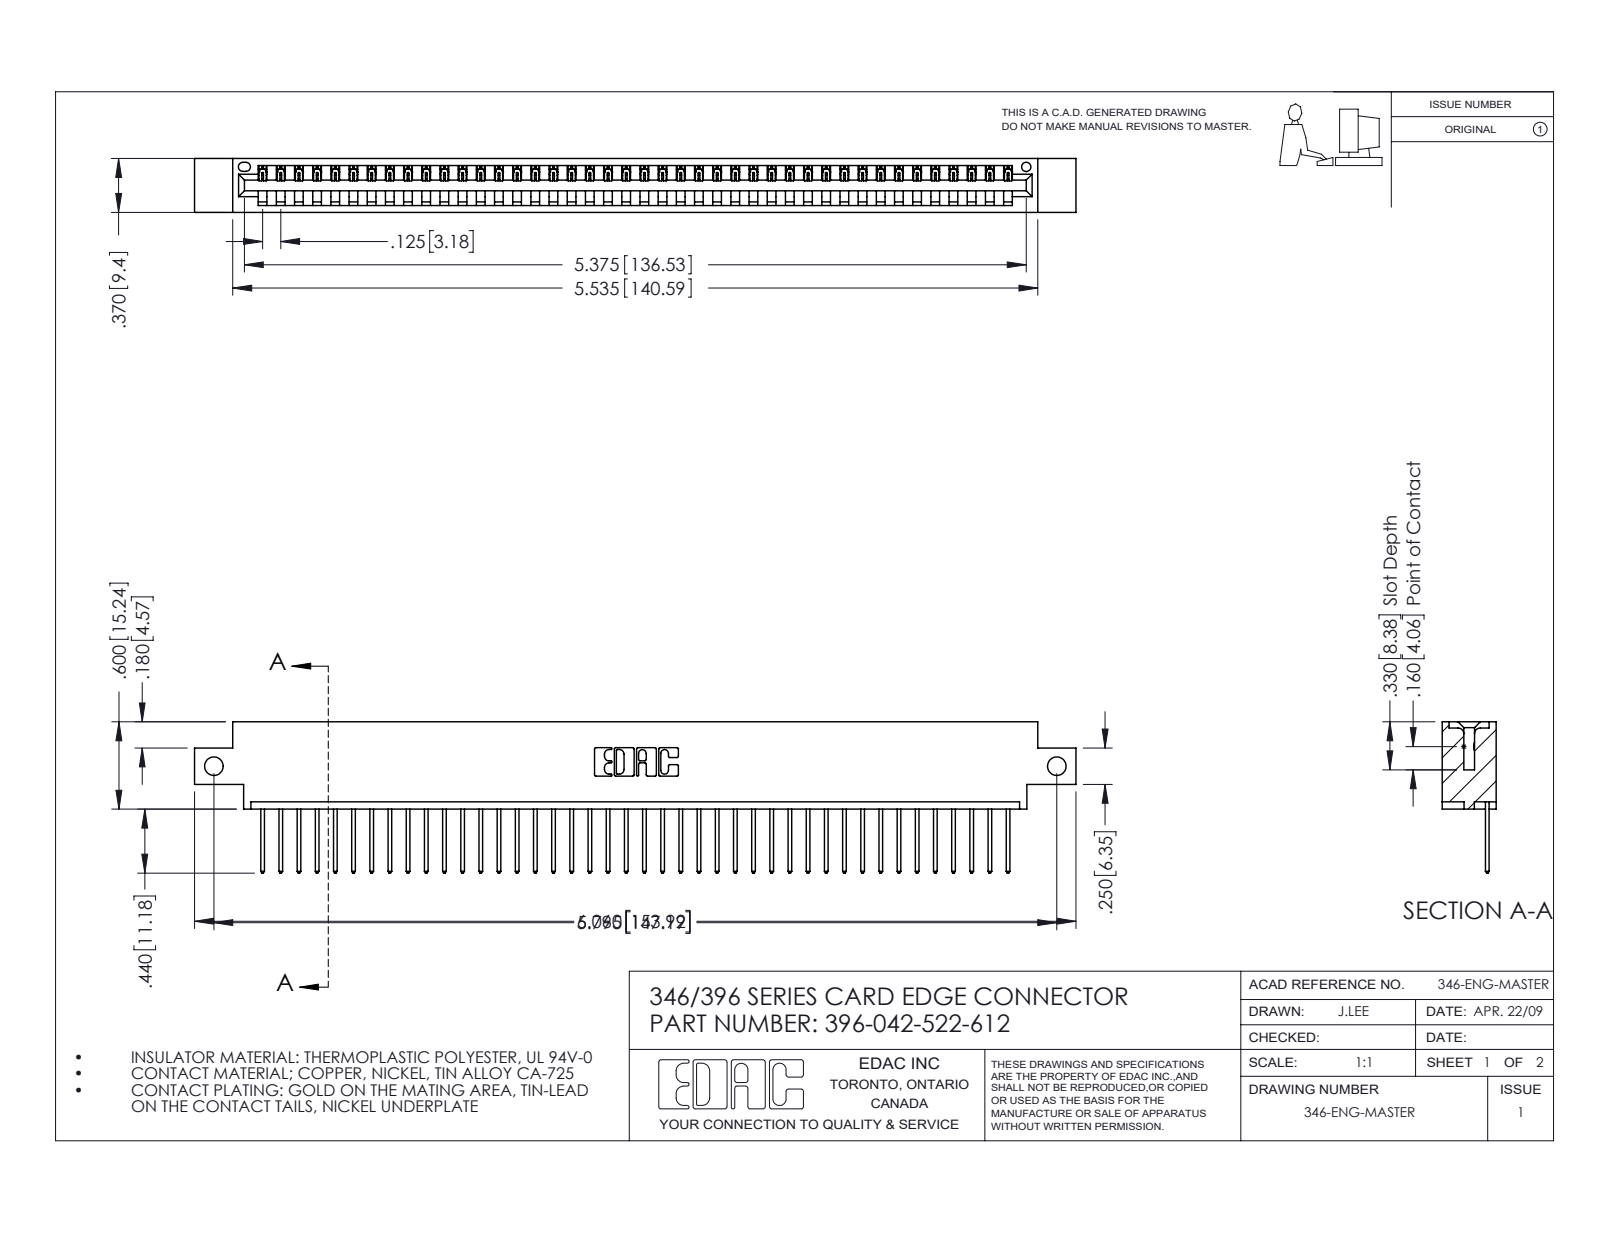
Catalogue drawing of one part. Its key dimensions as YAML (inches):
part_name: "346 Part_0.170 Offset - Side Mount; 345-292-001_345-293-122; 396-042-522-612"
step_written_by: "SolidWorks 2016 (CONFIG_CONTROL_DESIGN)"
units: inches
bodies: {solids: 43, faces: 2562, planar: 1760, cylindrical: 802, other: 0}
overall_size: [6.06, 1.04, 0.37]
volume: 0.885
surface_area: 28.35
round_holes:
  - {diameter: 0.128, count: 2}
  - {diameter: 0.064, count: 1}
partial_cylinders:
  - {radius: 0.006, count: 84}
  - {radius: 0.01, count: 84}
  - {radius: 0.01, count: 22}
  - {radius: 0.007, count: 6}
  - {radius: 0.031, count: 6}
  - {radius: 0.026, count: 3}
  - {radius: 0.031, count: 2}
  - {radius: 0.04, count: 2}
face_to_face_distances: [0.048, 0.322, 0.37, 0.25, 0.072, 0.298, 0.025, 0.148, 0.222, 0.1]
hole_center_spacings: [5.795]
